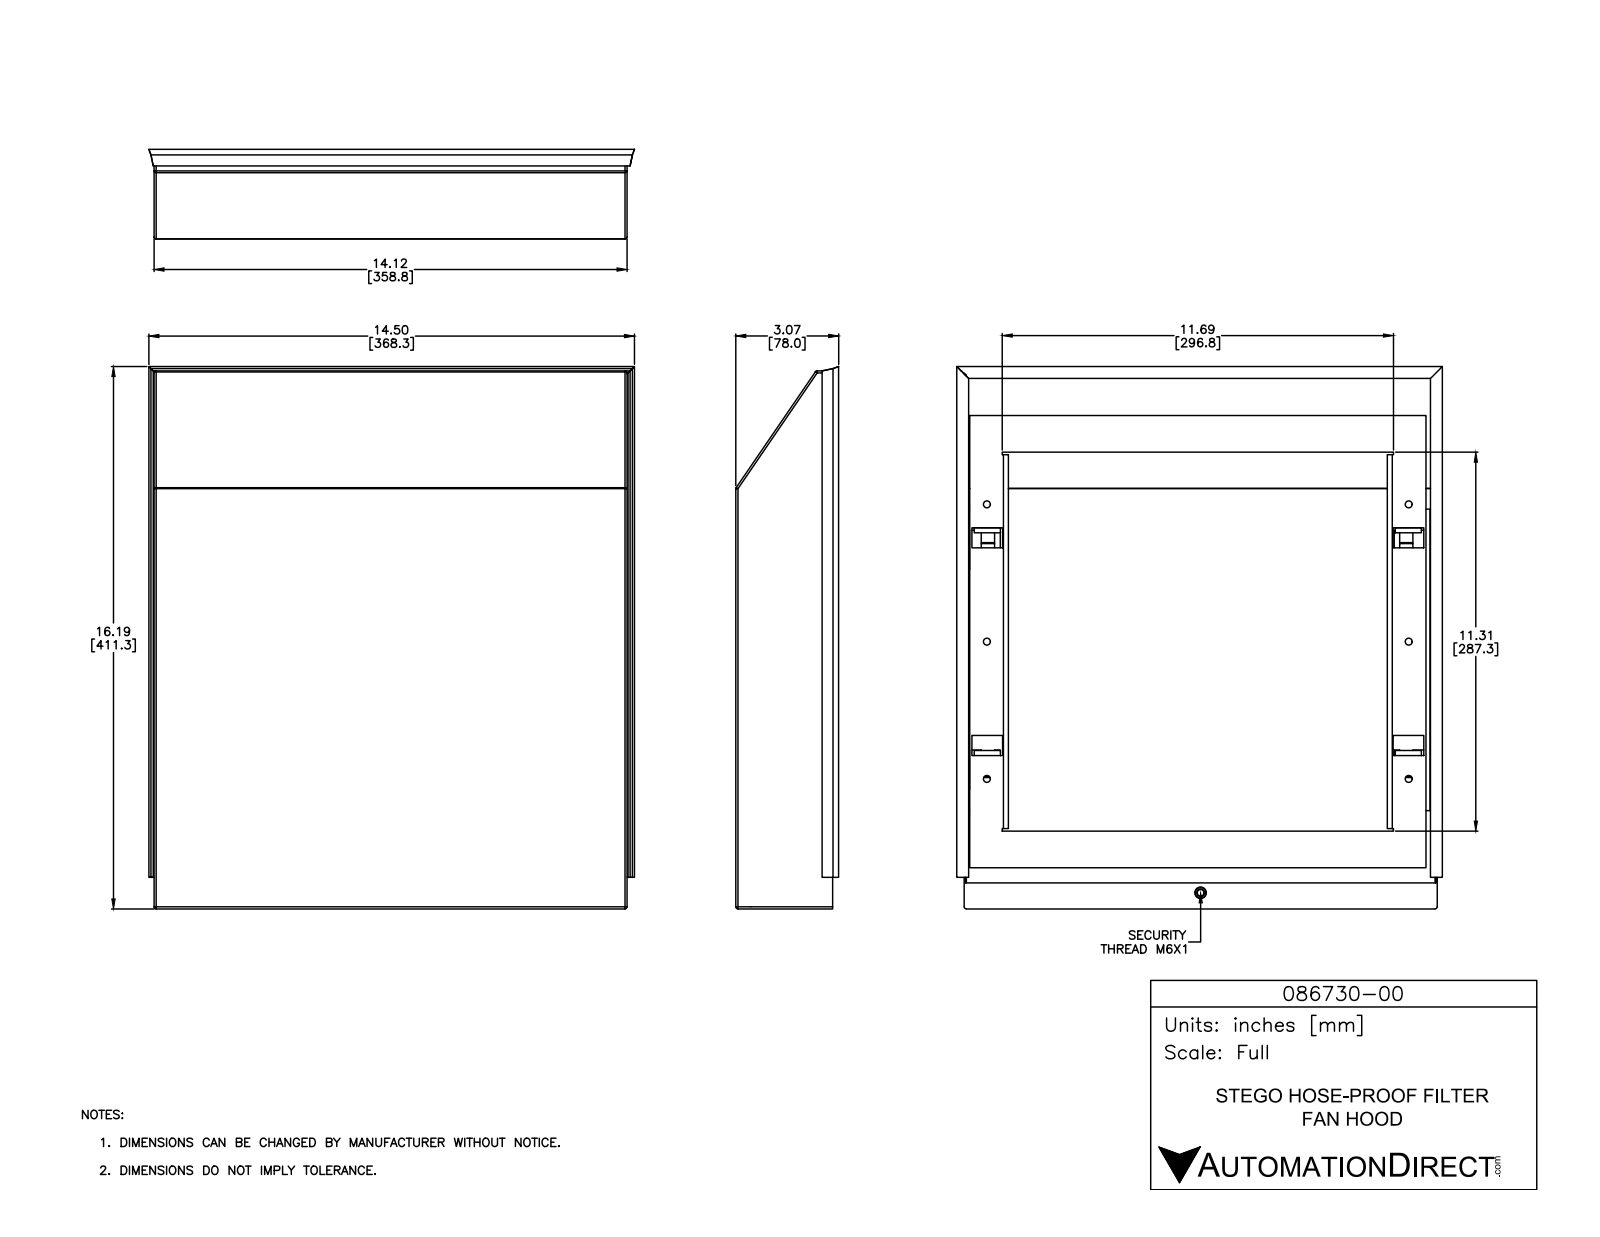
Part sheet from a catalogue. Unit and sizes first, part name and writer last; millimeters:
Units: millimetres
Overall size (bounding box): 411.3 × 368.3 × 82.6
Round holes (diameter × count): ⌀5.2 ×6, ⌀5 ×1, ⌀8.8 ×1
Partial cylindrical surfaces — rounded edges, fillets, slot ends (radius × count): R5 ×54, R0.6 ×11, R1.6 ×11, R1.9 ×4, R2.3 ×4, R3.8 ×4, R4.6 ×4, R9.1 ×3
Main face-to-face distances: 0.9, 357.8, 1.9, 82.5, 81.6, 80.6, 79.7, 356.9, 358.8, 2.3
Hole centre spacings: 336.6, 320, 104.1, 104.1, 208.2, 381.8, 181.1, 184.8
Volume: 378 200 mm³ · Surface area: 651 600 mm²
Bodies: 10 solids, 421 faces (293 planar, 112 cylindrical, 16 other)
Part name (STEP PRODUCT): 086730-00; 086730-004; 086730-003; GASKET (+5 more)
STEP written by: Autodesk Inventor 2018 (AUTOMOTIVE_DESIGN)
